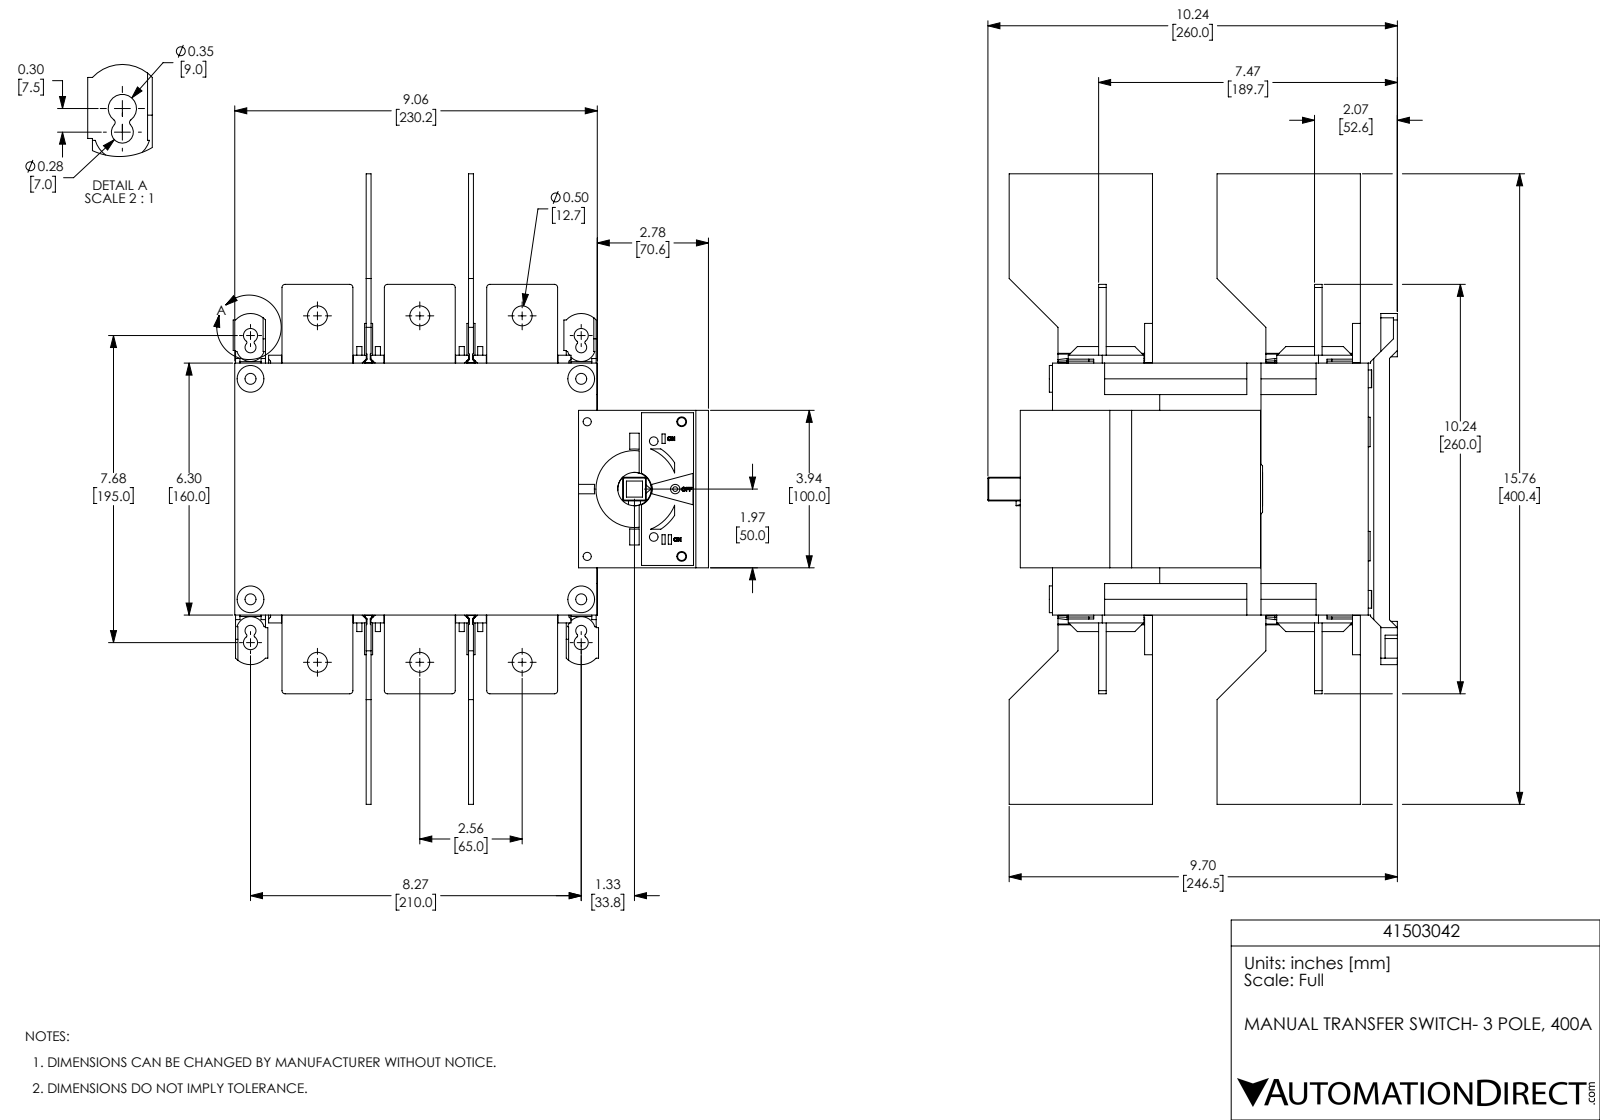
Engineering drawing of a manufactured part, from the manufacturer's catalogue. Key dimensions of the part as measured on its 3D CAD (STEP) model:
Part name (STEP PRODUCT): 41503042
STEP written by: SolidWorks 2017 (AUTOMOTIVE_DESIGN)
Units: inches
Bodies: 11 solids, 1480 faces (1182 planar, 292 cylindrical, 6 other)
Overall size (bounding box): 15.764 × 11.882 × 10.236
Volume: 492 in³ · Surface area: 1 011 in²
Round holes (diameter × count): ⌀0.248 ×12, ⌀0.5 ×6, ⌀0.205 ×4, ⌀0.276 ×4, ⌀0.354 ×4, ⌀0.472 ×4, ⌀0.217 ×2, ⌀0.118 ×1, ⌀0.839 ×1, ⌀0.846 ×1
Round bosses / shafts (diameter × count): ⌀0.669 ×4, ⌀0.833 ×1, ⌀0.236 ×1
Partial cylindrical surfaces — rounded edges, fillets, slot ends (radius × count): R0.079 ×12, R0.344 ×12, R0.039 ×8, R0.217 ×8, R0.02 ×4, R0.049 ×4, R0.138 ×4, R0.236 ×4
Main face-to-face distances: 0.122, 2.559, 2.681, 2.437, 6.299, 7.894, 3.285, 0.189, 3.407, 5.844
Hole centre spacings: 2.559, 8.268, 2.056, 5.118, 8.655, 9.031, 1.083, 1.291
